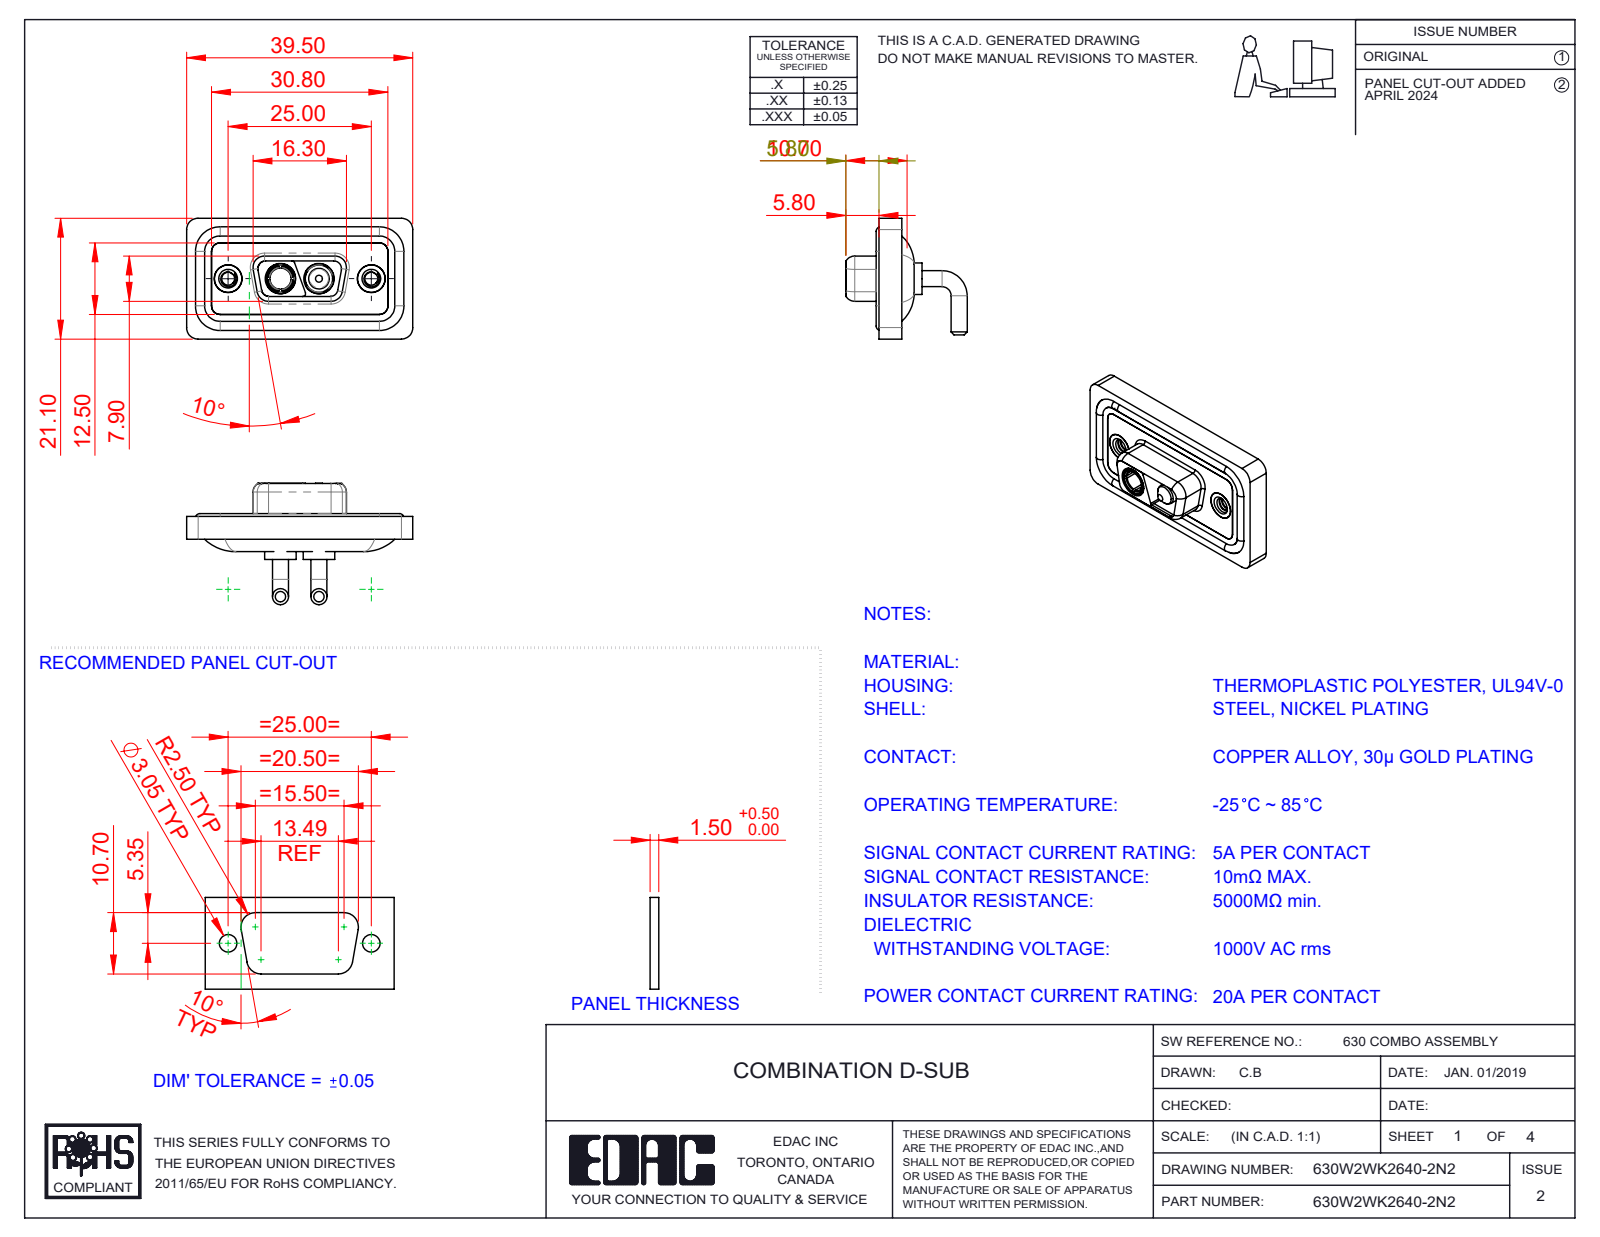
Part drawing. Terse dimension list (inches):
name: Power Socket_20A RA; 630Combo Waterproof Housing_09 Contacts; 630Combo Shell Front_09 Contacts; 630Combo Shell Rear_09 Contacts (+4 more)
written by: SolidWorks 2023 (CONFIG_CONTROL_DESIGN)
unit: in
bodies: 11 solids, 508 faces (144 planar, 235 cylindrical, 129 other)
size: 1.555 × 0.835 × 0.831
volume: 0.287 in³; area: 11.62 in²
holes: 4× ⌀0.191, 2× ⌀0.089, 2× ⌀0.157, 2× ⌀0.159, 2× ⌀0.197, 2× ⌀0.209, 1× ⌀0.146
bosses: 4× ⌀0.11, 4× ⌀0.063, 2× ⌀0.217, 2× ⌀0.205, 2× ⌀0.195, 2× ⌀0.189, 2× ⌀0.187, 2× ⌀0.148
rounds: 18× R0.059, 18× R0.079, 8× R0.053, 8× R0.063, 6× R0.02, 4× R0.01, 4× R0.024, 4× R0.026
face distances: 0.016, 0.043, 0.114, 0.071, 0.098, 0.063, 0.122, 0.059, 0.083, 0.146
hole spacings: 0.36, 0.624, 0.265, 0.984
